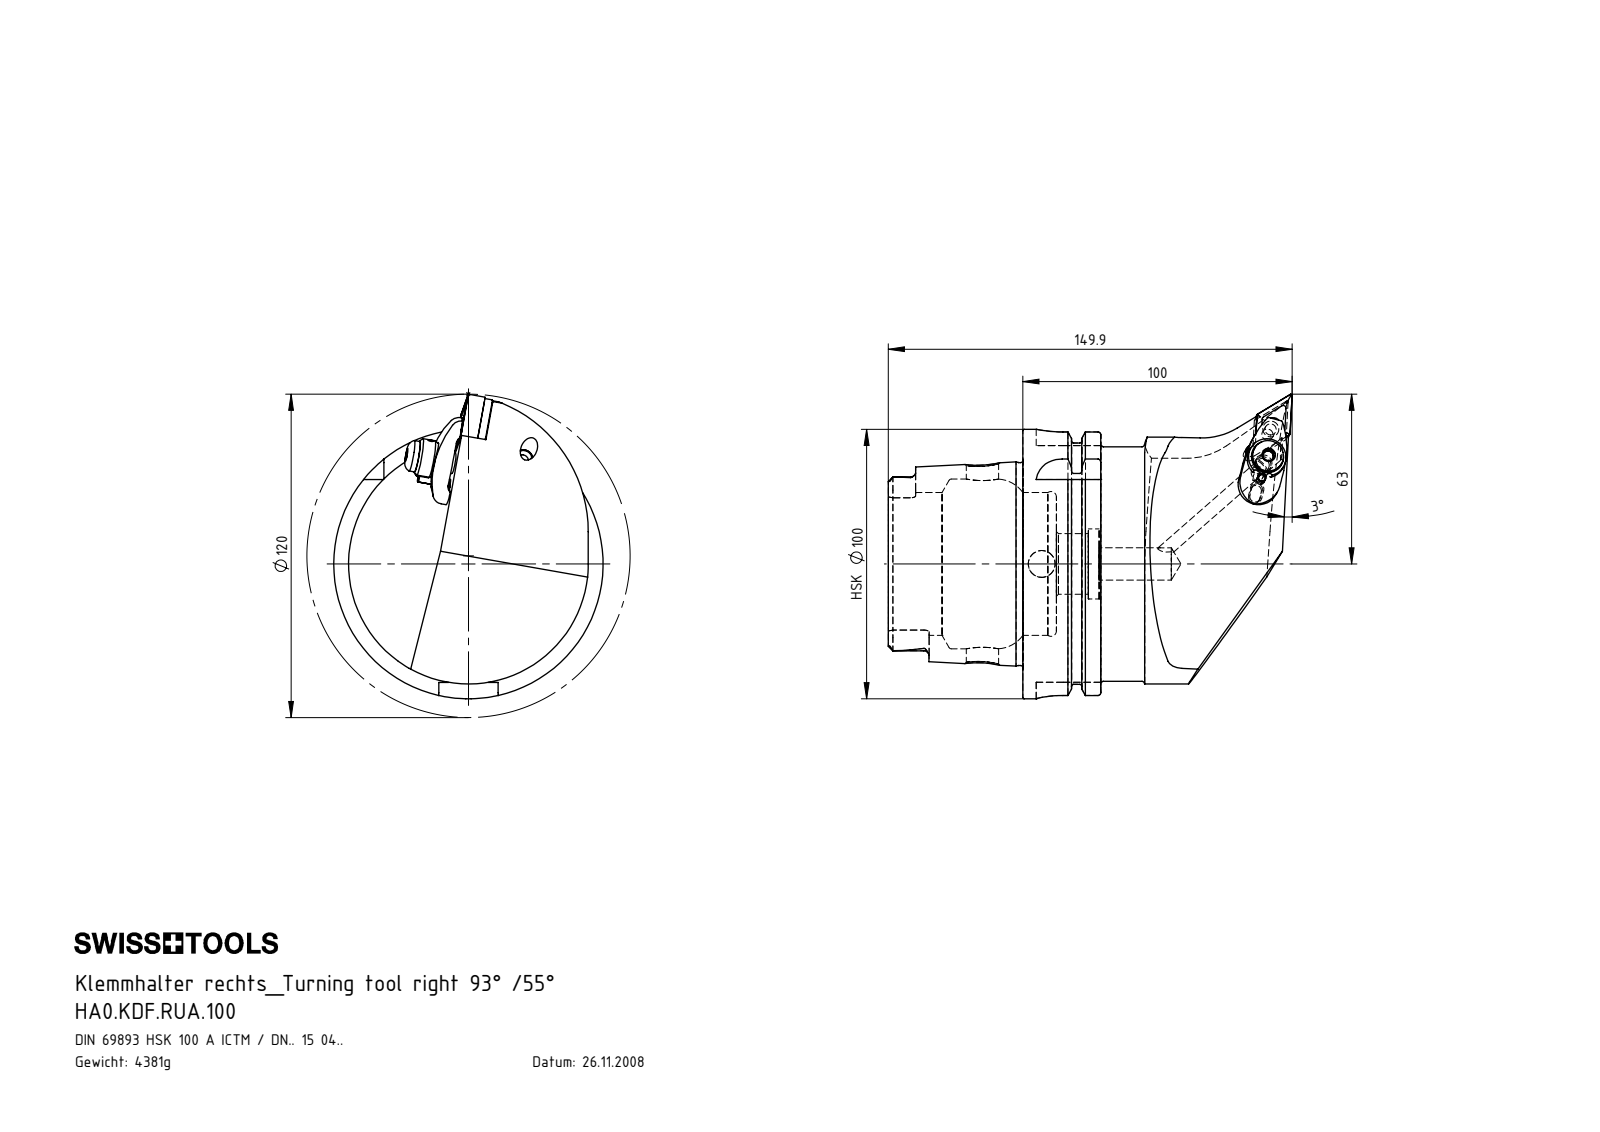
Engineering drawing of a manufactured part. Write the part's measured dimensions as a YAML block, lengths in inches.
part_name: "HA0-KDF.RUA.100_A_Fertigbearbeitung; WCC-ER3.102.024_C; WCC-ER4.103.032_A; WCC-ER5.102.012_B (+7 more)"
step_written_by: "SolidWorks 2017 (AUTOMOTIVE_DESIGN)"
units: inches
bodies: {solids: 11, faces: 469, planar: 122, cylindrical: 154, other: 193}
overall_size: [5.902, 4.449, 3.937]
volume: 34.11
surface_area: 114.9
round_holes:
  - {diameter: 0.079, count: 3}
  - {diameter: 0.197, count: 3}
  - {diameter: 0.244, count: 2}
  - {diameter: 0.276, count: 2}
  - {diameter: 0.472, count: 2}
  - {diameter: 0.094, count: 1}
  - {diameter: 0.118, count: 1}
  - {diameter: 0.165, count: 1}
  - {diameter: 0.203, count: 1}
  - {diameter: 0.236, count: 1}
  - {diameter: 0.256, count: 1}
  - {diameter: 0.335, count: 1}
round_bosses_or_shafts:
  - {diameter: 0.236, count: 2}
  - {diameter: 0.118, count: 2}
  - {diameter: 3.937, count: 1}
  - {diameter: 3.62, count: 1}
  - {diameter: 3.425, count: 1}
  - {diameter: 2.963, count: 1}
  - {diameter: 0.551, count: 1}
  - {diameter: 0.453, count: 1}
partial_cylinders:
  - {radius: 0.015, count: 6}
  - {radius: 0.027, count: 6}
  - {radius: 0.075, count: 6}
  - {radius: 0.016, count: 4}
  - {radius: 0.394, count: 4}
  - {radius: 0.059, count: 3}
  - {radius: 0.079, count: 2}
  - {radius: 0.118, count: 2}
face_to_face_distances: [0.49, 0.65, 1.14, 1.965, 2.455, 3.104, 0.481, 3.457, 3.079, 1.114]
hole_center_spacings: [0.311, 0.311, 0.591, 0.594, 0.311, 0.312, 0.322, 0.323]
